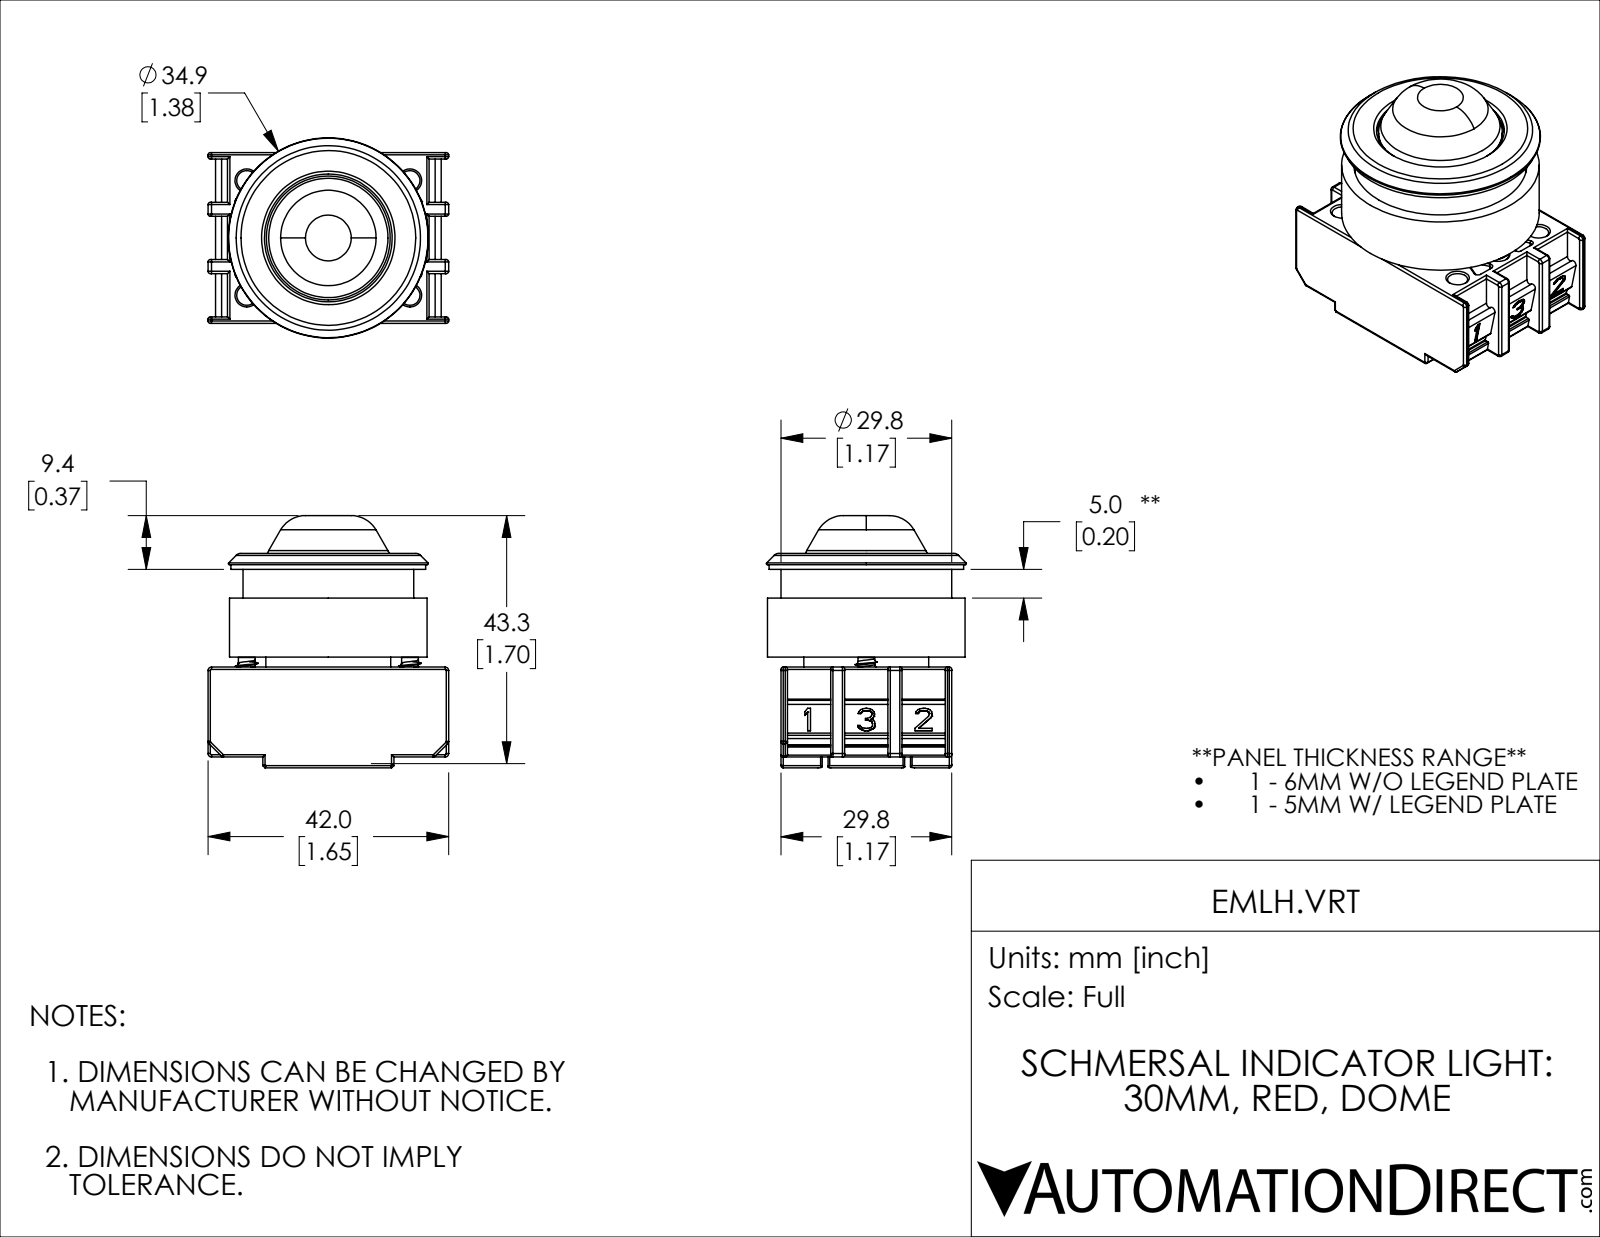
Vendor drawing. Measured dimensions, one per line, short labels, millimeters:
name: EMLH.VRT
written by: SolidWorks 2019 (CONFIG_CONTROL_DESIGN)
unit: mm
bodies: 3 solids, 1622 faces (641 planar, 498 cylindrical, 483 other)
size: 44.05 × 42 × 34.93
volume: 22 577 mm³; area: 22 231 mm²
holes: 6× ⌀3.5, 6× ⌀5.15, 1× ⌀11, 1× ⌀12.6, 1× ⌀15, 1× ⌀18, 1× ⌀22.3, 1× ⌀24.2, 1× ⌀26, 1× ⌀27, 1× ⌀30.2
bosses: 2× ⌀4.8, 2× ⌀2.93, 1× ⌀34.5, 1× ⌀34, 1× ⌀29.8, 1× ⌀25.5, 1× ⌀24.5, 1× ⌀23.8
rounds: 115× R0.4, 48× R0.3, 28× R0.2, 8× R0.6, 6× R0.5, 2× R0.1, 2× R0.6, 2× R0.8
face distances: 29.8, 1.75, 1.9, 19.35, 19.85, 18.1, 10, 3.4, 7.8, 4.4
hole spacings: 10, 17.41, 30.2, 28.5, 14.25, 20, 34.82
